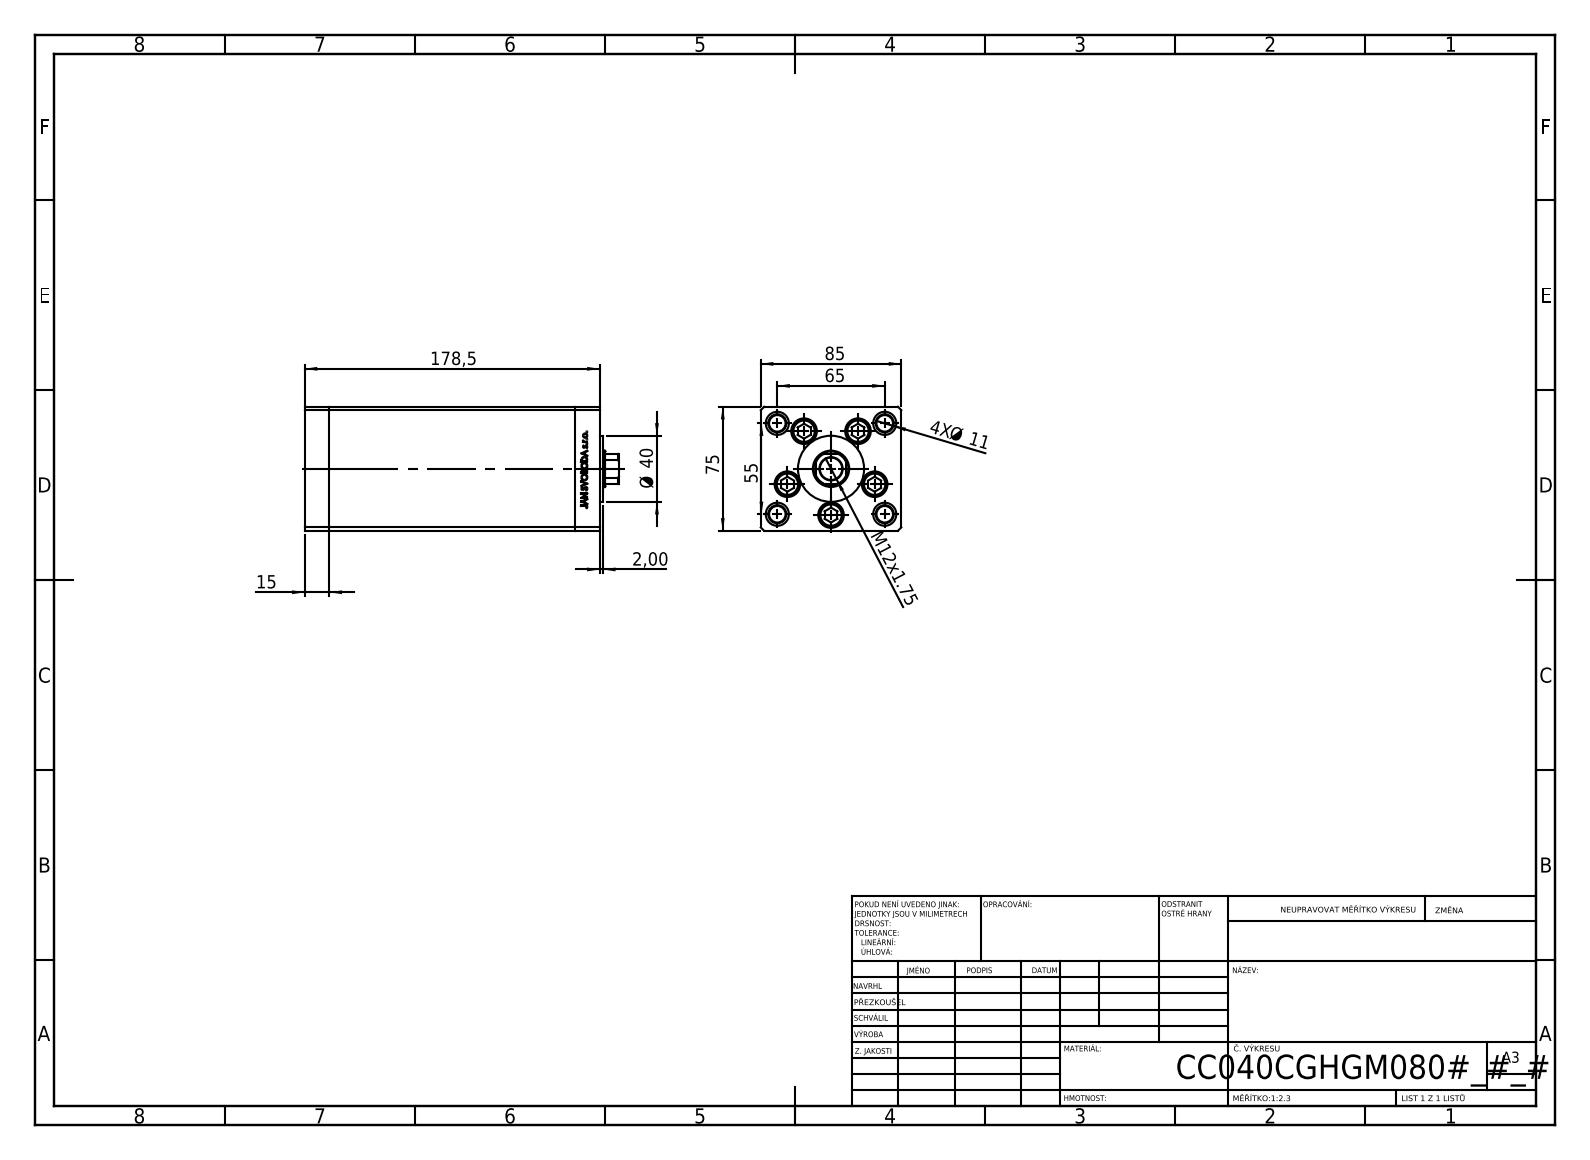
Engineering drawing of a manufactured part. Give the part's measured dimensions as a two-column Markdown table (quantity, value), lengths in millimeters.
| quantity | value |
| --- | --- |
| part name | V220C BACK_C; V220C_C MIDDLE; V220C_VC_C; V220C FRONT (+1 more) |
| STEP written by | SolidWorks 2019 (CONFIG_CONTROL_DESIGN) |
| units | millimeters |
| bodies | 13 solids, 1181 faces (544 planar, 175 cylindrical, 462 other) |
| overall size | 190 × 85 × 75 |
| volume | 941 731 mm³ |
| surface area | 181 774 mm² |
| round holes (diameter × count) | 11 × 9, 15.5 × 5, 2 × 4, 10 × 4, 13.16 × 4, 14 × 4, 13.5 × 1, 14.5 × 1, 22 × 1 |
| round bosses / shafts (diameter × count) | 8 × 5, 14.5 × 4, 40 × 1 |
| partial cylindrical surfaces (radius × count) | 0.93 × 2, 10.5 × 1 |
| main face-to-face distances | 85, 75, 15, 148.5, 163.5, 10.5, 178.5, 34.25, 144.25, 129.25 |
| hole center spacings | 28, 42.57, 16.86, 19.17, 32.33, 32.5, 33.63, 37.33 |
